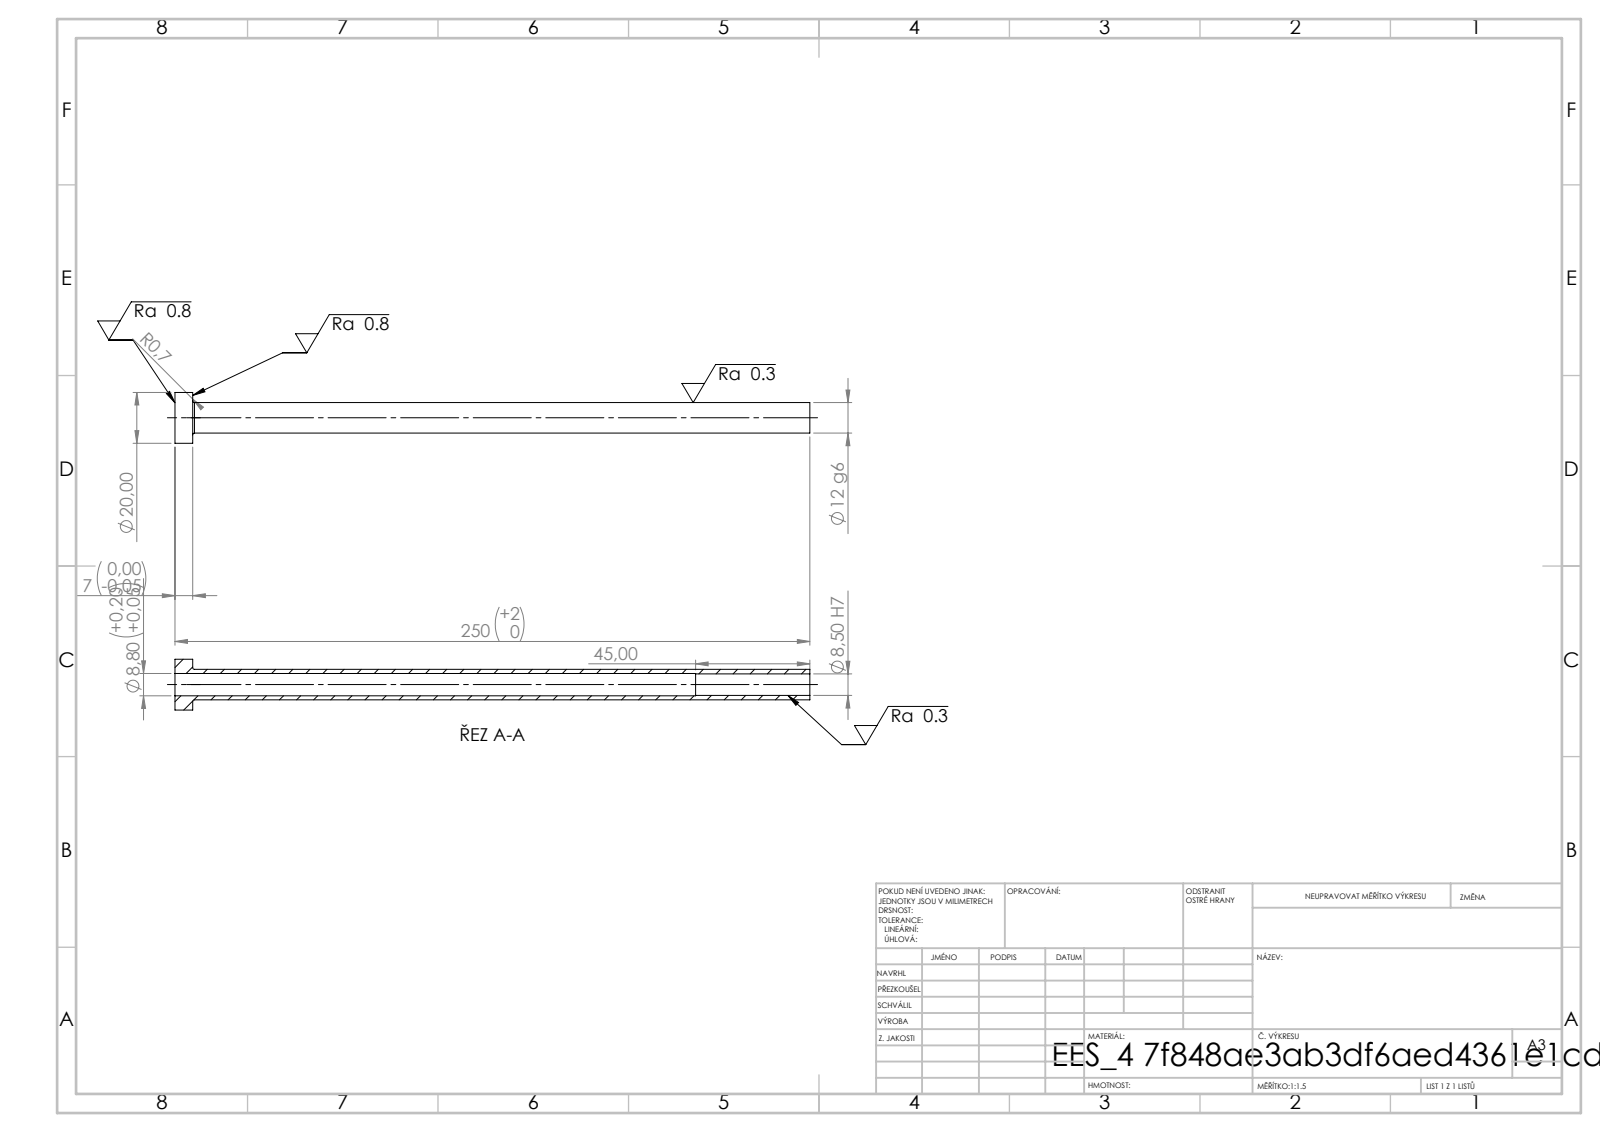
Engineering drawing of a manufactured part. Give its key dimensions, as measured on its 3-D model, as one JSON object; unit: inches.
{"step_written_by": "SolidWorks 2019 (CONFIG_CONTROL_DESIGN)", "units": "inches", "bodies": {"solids": 1, "faces": 14, "planar": 4, "cylindrical": 8, "other": 2}, "overall_size": [9.843, 0.787, 0.787], "volume_in3": 0.895, "surface_area_in2": 26.31, "round_holes": [[0.335, 1], [0.346, 1]], "round_bosses_or_shafts": [[0.787, 1], [0.472, 1]], "face_to_face_distances": [0.276, 9.843, 9.567, 8.071, 7.795, 1.772]}
